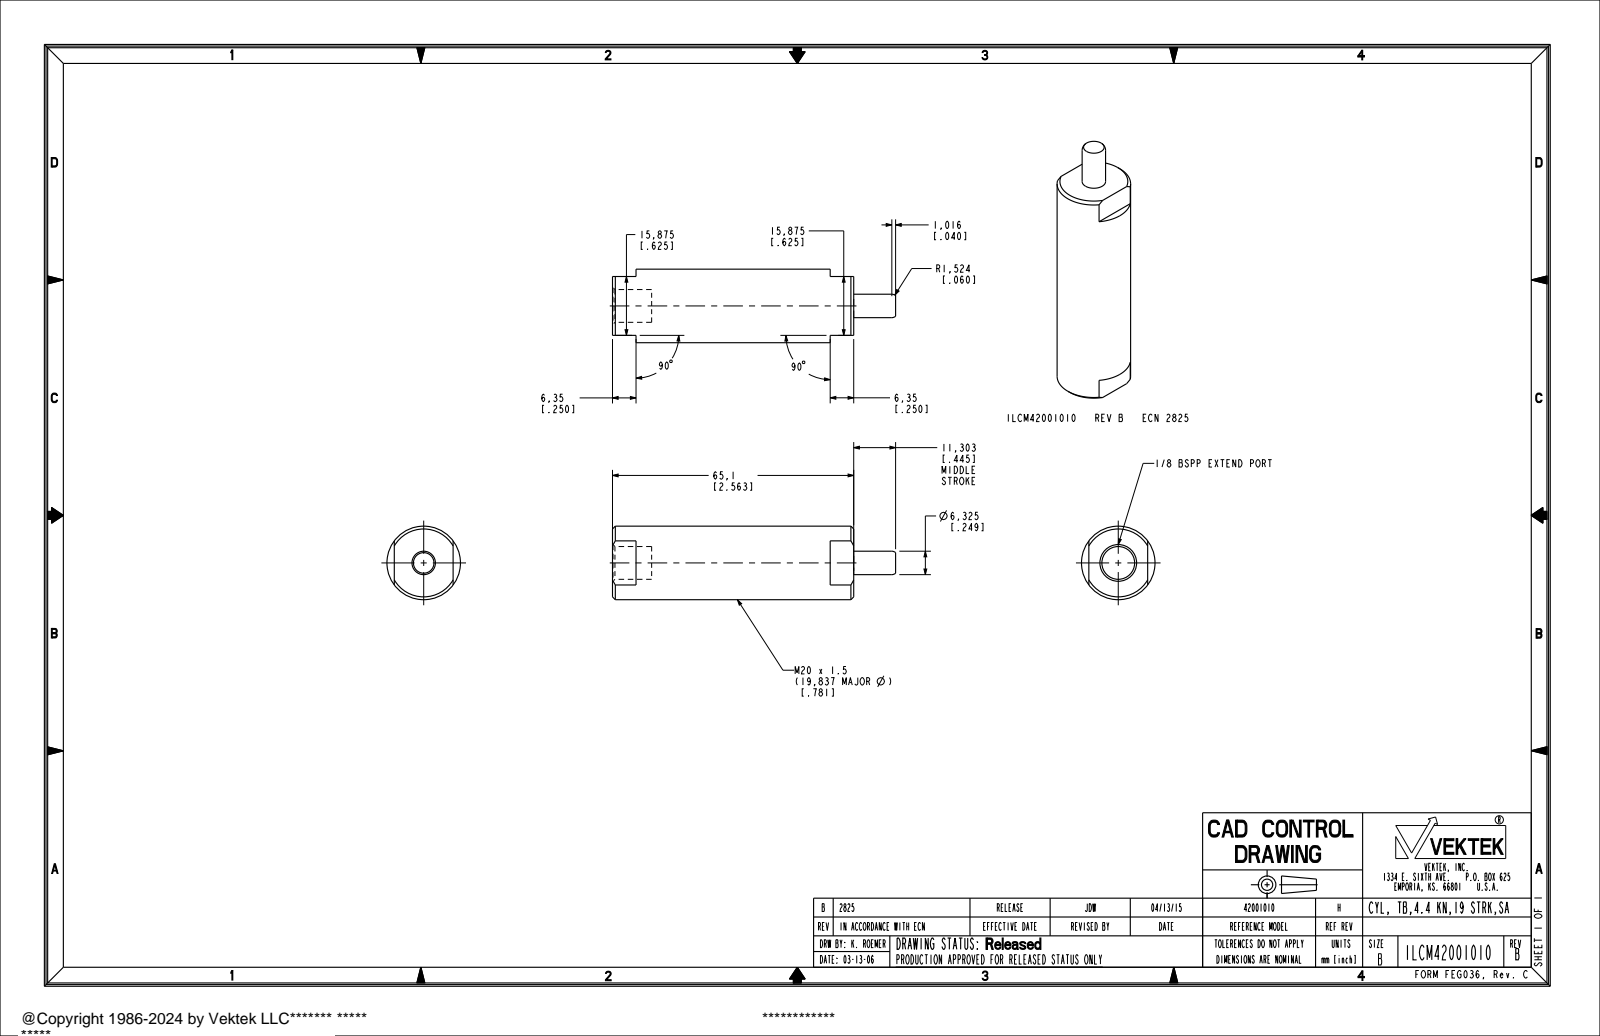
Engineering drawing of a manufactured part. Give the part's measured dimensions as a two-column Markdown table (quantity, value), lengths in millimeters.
| quantity | value |
| --- | --- |
| part name | ILCM42001010 |
| STEP written by | PRO/ENGINEER BY PARAMETRIC TECHNOLOGY CORPORATION, 2013320 (AUTOMOTIVE_DESIGN) |
| units | millimeters |
| bodies | 1 solid, 28 faces (12 planar, 8 cylindrical, 8 other) |
| overall size | 76.4 × 19.84 × 19.84 |
| volume | 19 389 mm³ |
| surface area | 5 121 mm² |
| round holes (diameter × count) | 8.84 × 1, 9.91 × 1 |
| round bosses / shafts (diameter × count) | 19.84 × 1, 6.33 × 1 |
| main face-to-face distances | 65.1, 15.88, 6.35, 58.75, 10.57, 54.53, 48.18, 4.22, 52.4, 76.4 |
